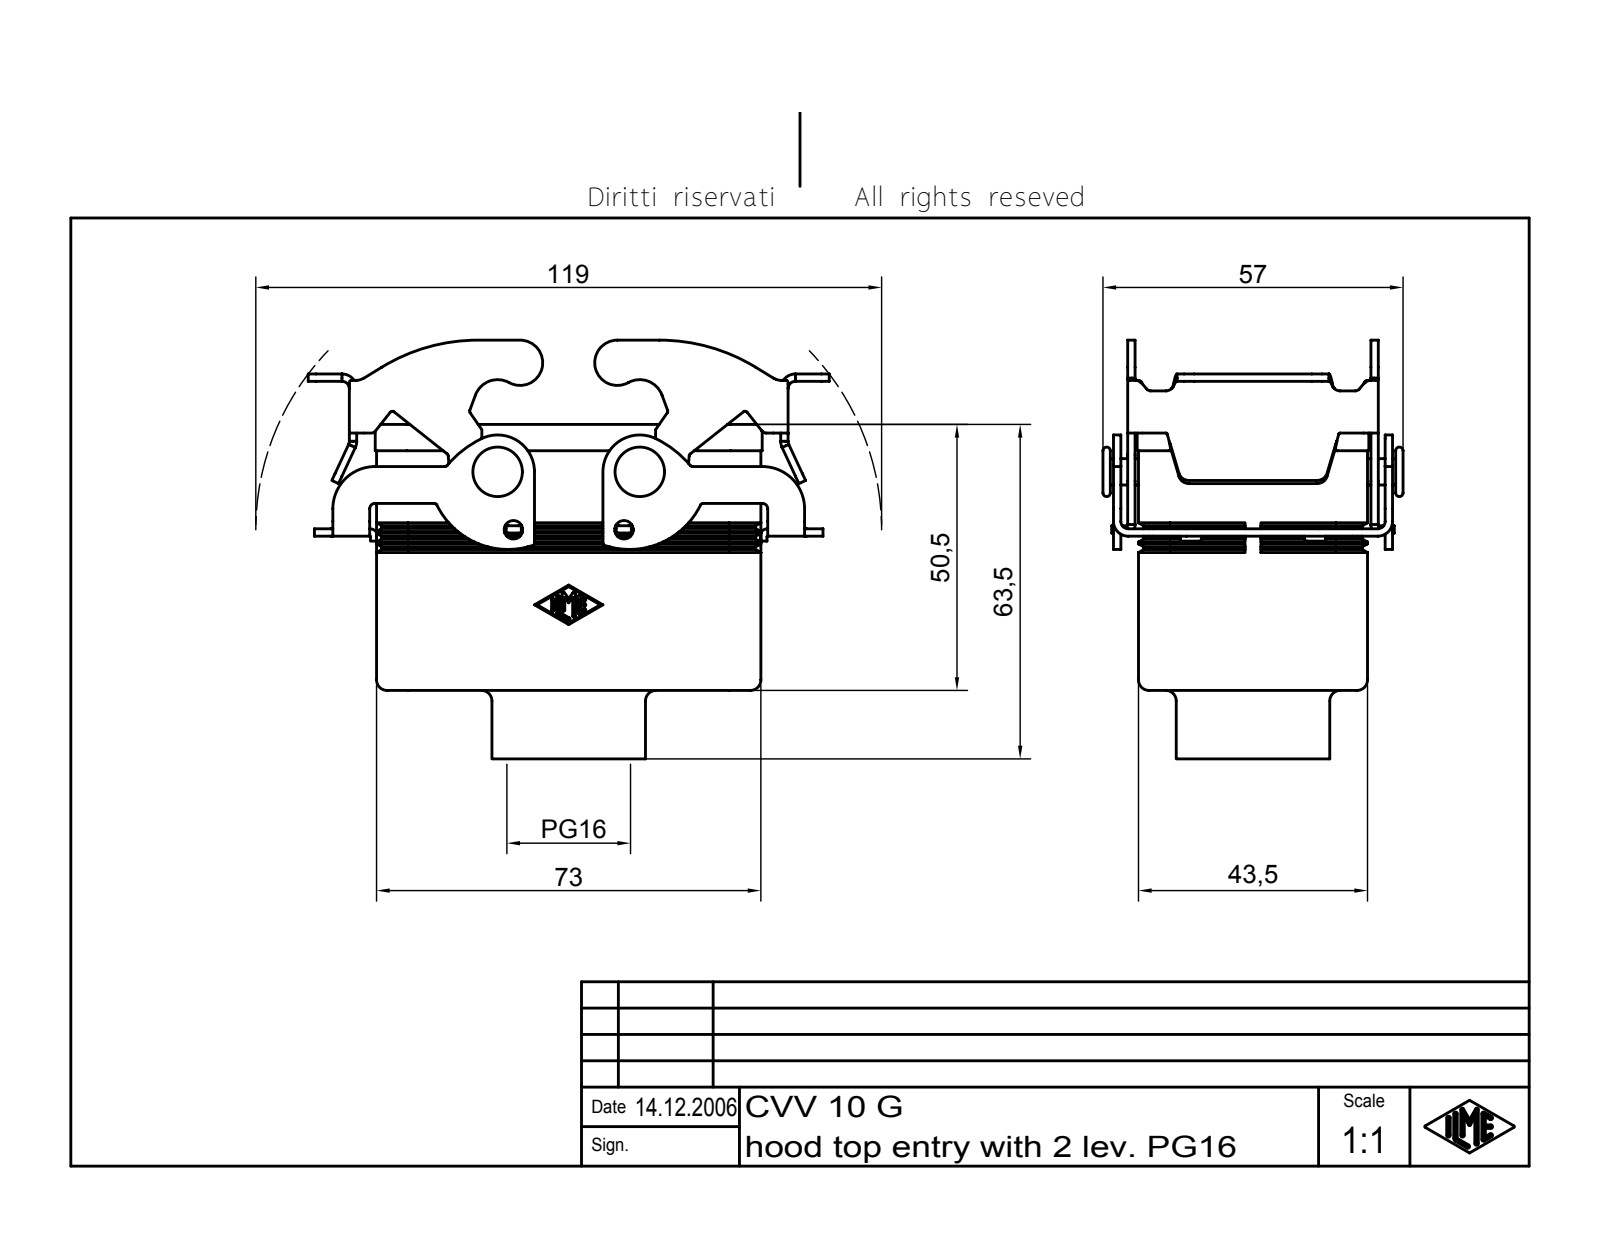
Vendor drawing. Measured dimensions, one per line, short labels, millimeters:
name: CVV 10 G
written by: Autodesk Inventor 7 (AUTOMOTIVE_DESIGN)
unit: mm
bodies: 3 solids, 714 faces (207 planar, 186 cylindrical, 321 other)
size: 98.97 × 79.5 × 57
volume: 63 778 mm³; area: 47 074 mm²
holes: 2× ⌀3.5, 1× ⌀18.16, 1× ⌀21.16
bosses: 2× ⌀5, 2× ⌀3.2, 1× ⌀29.16
rounds: 18× R0.5, 16× R0.25, 14× R1, 12× R1.5, 12× R2, 10× R1.4, 10× R2.8, 8× R6
face distances: 3, 40.5, 1.4, 43.5, 37.5, 70, 2.7, 48.9, 47.5, 8.5
hole spacings: 21
